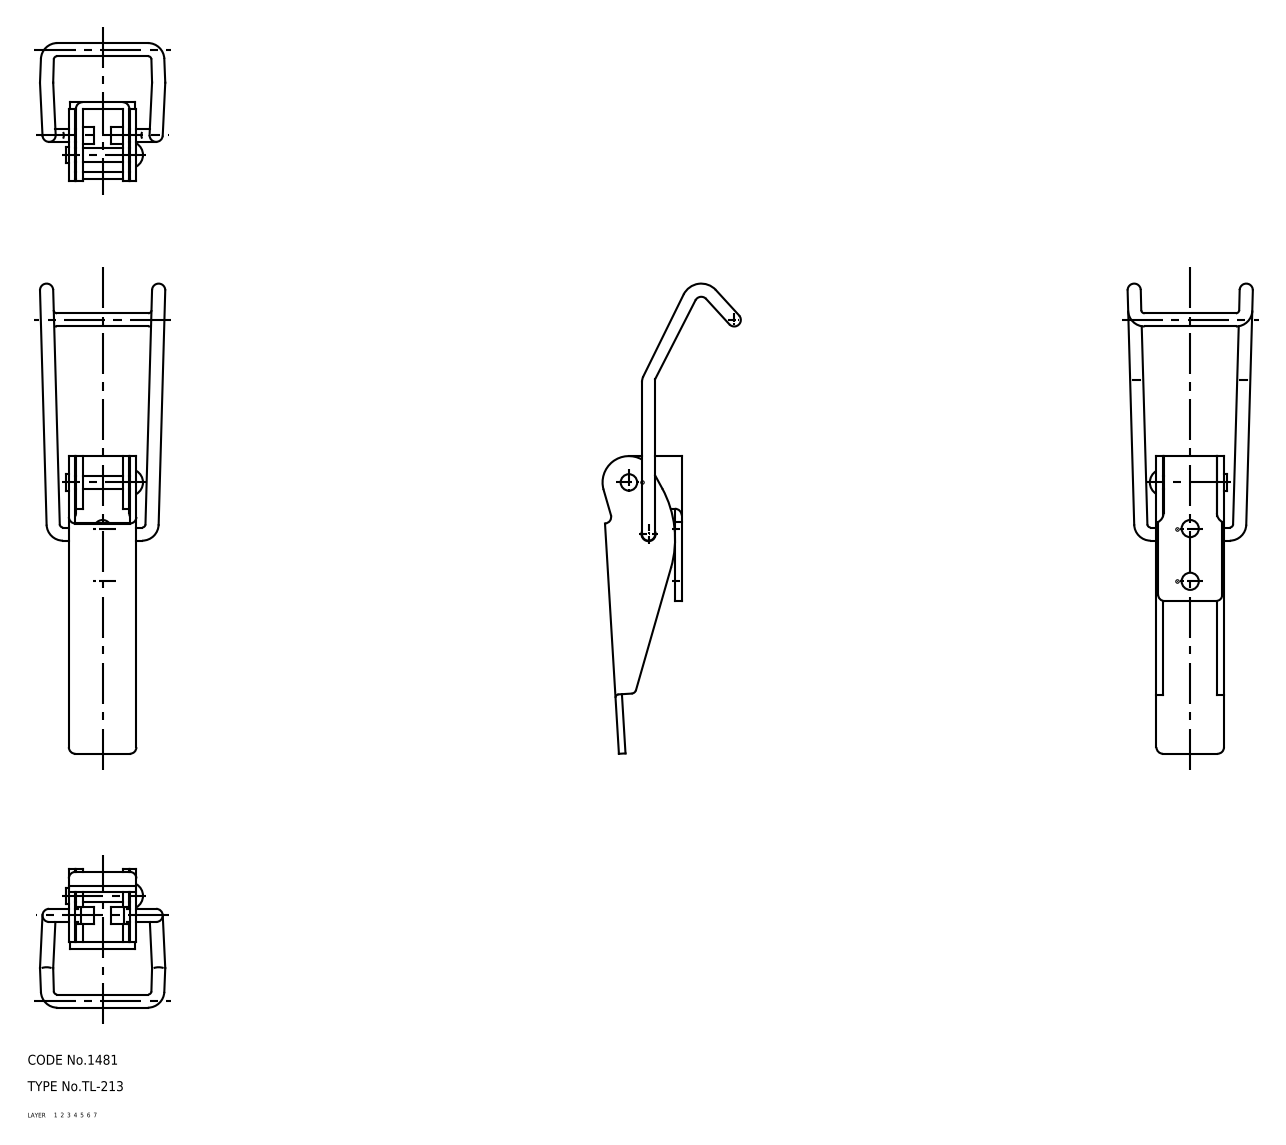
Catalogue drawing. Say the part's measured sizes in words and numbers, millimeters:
The part is named "arm; rivet; lever; base (+1 more)". Its 3-D file was written by "CADfix (AUTOMOTIVE_DESIGN)". It is 4 solids with 110 faces: 0 planar, 0 cylindrical and 110 other. Overall it measures 142.71 by 41.96 by 38 millimeters. Its volume is 12 631 cubic millimeters and its surface area 13 923 square millimeters.
